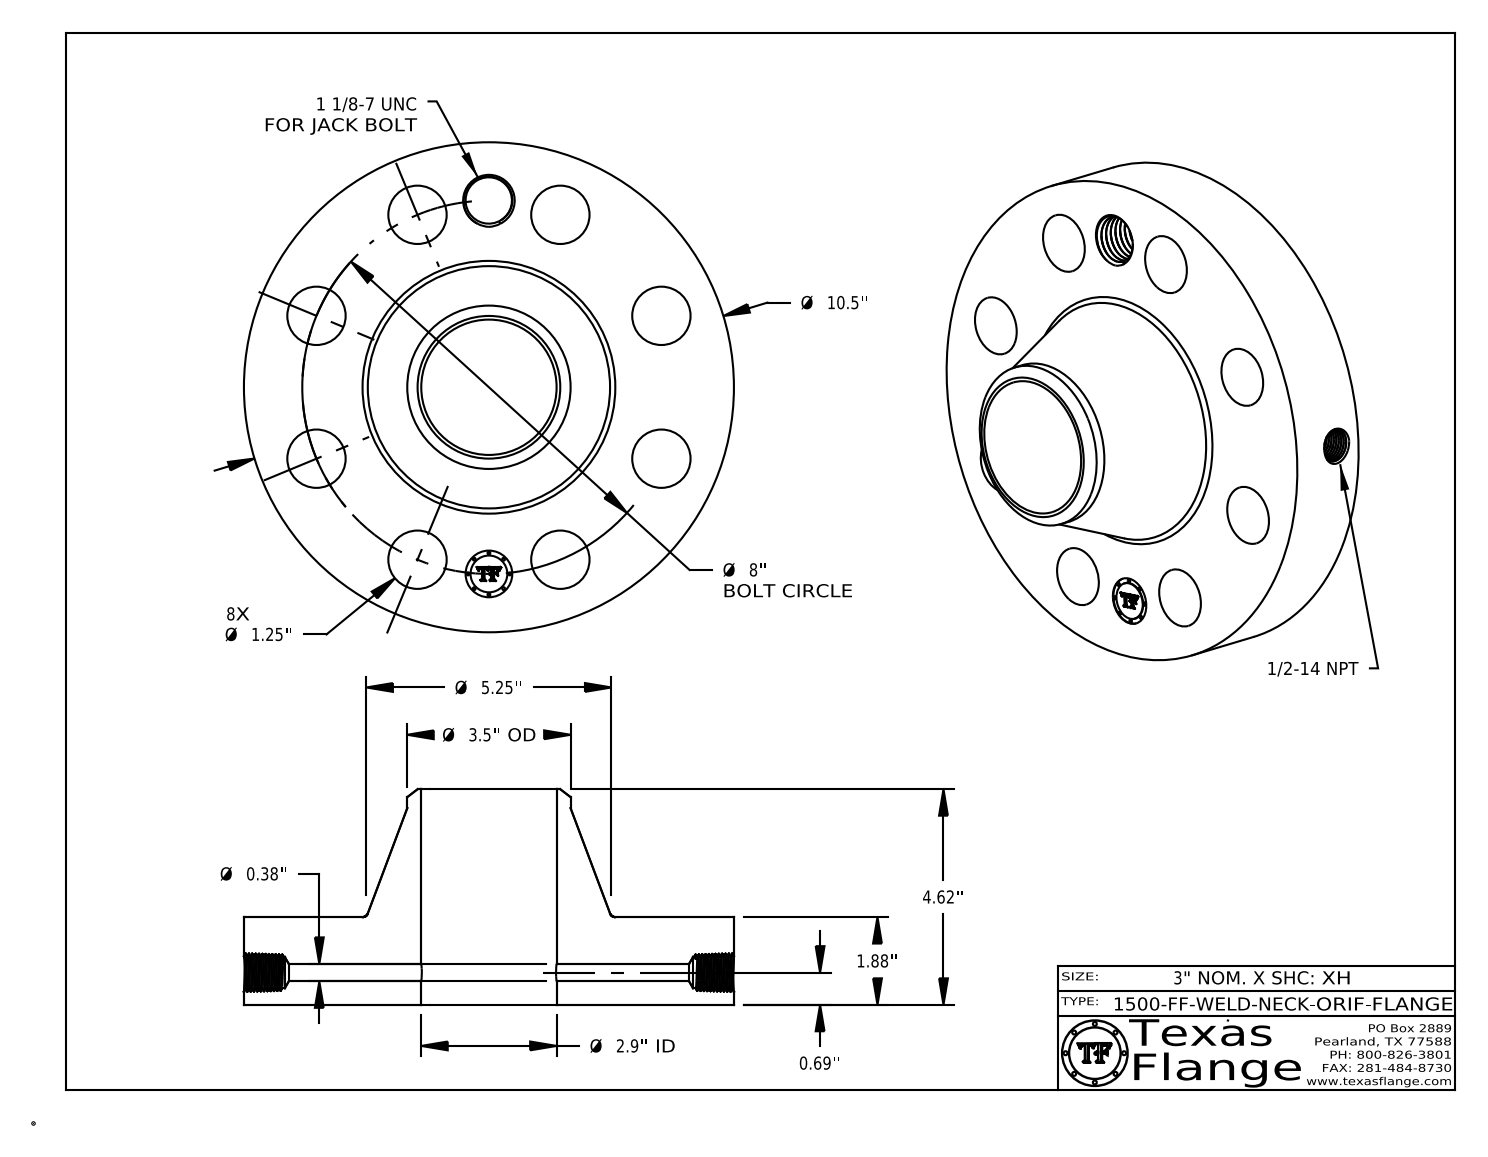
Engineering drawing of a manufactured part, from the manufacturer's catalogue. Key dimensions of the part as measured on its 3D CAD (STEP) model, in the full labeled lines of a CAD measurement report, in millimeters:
Part name (STEP PRODUCT): 1500-FF-WELD-NECK
STEP written by: CATIA V5 STEP AP214 (AUTOMOTIVE_DESIGN)
Units: millimetres
Bodies: 1 solid, 757 faces (368 planar, 88 cylindrical, 301 other)
Overall size (bounding box): 266.7 × 266.7 × 117.3
Volume: 2 458 000 mm³ · Surface area: 225 200 mm²
Round holes (diameter × count): ⌀31.8 ×8, ⌀9.5 ×1, ⌀17.1 ×1, ⌀25 ×1, ⌀25.4 ×1, ⌀73.7 ×1
Round bosses / shafts (diameter × count): ⌀1.5 ×8, ⌀266.7 ×1, ⌀88.9 ×1, ⌀20 ×1
Main face-to-face distances: 47.8, 117.3, 69.6, 47.4, 0.4, 70, 7.6, 7.4, 1.4, 6.3
Hole centre spacings: 101.6, 143.7, 187.7, 39.6, 77.7, 77.8, 112.9, 169
